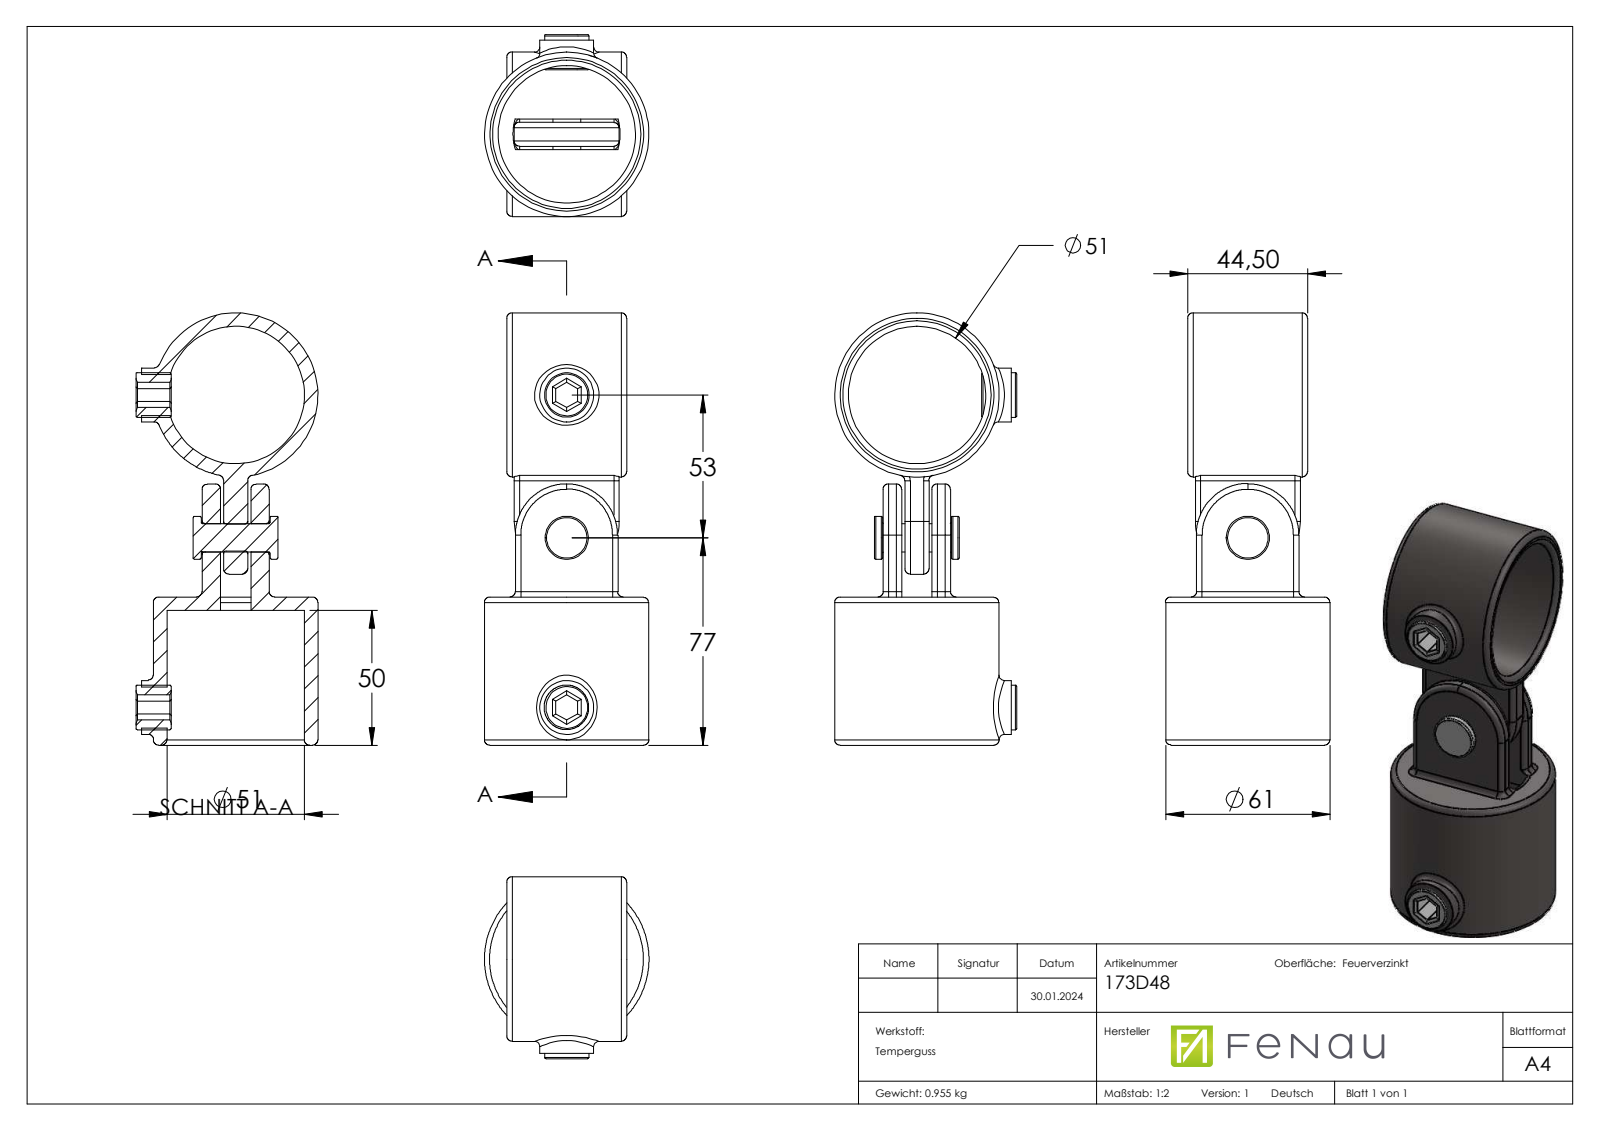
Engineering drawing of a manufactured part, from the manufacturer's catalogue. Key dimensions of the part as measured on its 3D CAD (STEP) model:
Part name (STEP PRODUCT): 173-D48 Teil1_173-D48 Teil1; 173-D48 Teil2_173-D48 Teil2; 173-D48 Teil4_173-D48 Teil4; 173-D48 (+1 more)
STEP written by: SolidWorks 2018 (CONFIG_CONTROL_DESIGN)
Units: millimetres
Bodies: 5 solids, 153 faces (39 planar, 67 cylindrical, 47 other)
Overall size (bounding box): 160.5 × 67.5 × 61
Volume: 130 233 mm³ · Surface area: 54 737 mm²
Round holes (diameter × count): ⌀15.25 ×2, ⌀51 ×2, ⌀10 ×1, ⌀10.5 ×1
Round bosses / shafts (diameter × count): ⌀61 ×2, ⌀20 ×2, ⌀16.5 ×2, ⌀16 ×1, ⌀10.4 ×1
Partial cylindrical surfaces — rounded edges, fillets, slot ends (radius × count): R2 ×38, R19 ×1, R19.5 ×1, R19.81 ×1
Main face-to-face distances: 6.9, 18.1, 8, 17, 1.1, 10.1, 11.2, 5, 25, 9
Hole centre spacings: 53, 63, 116
